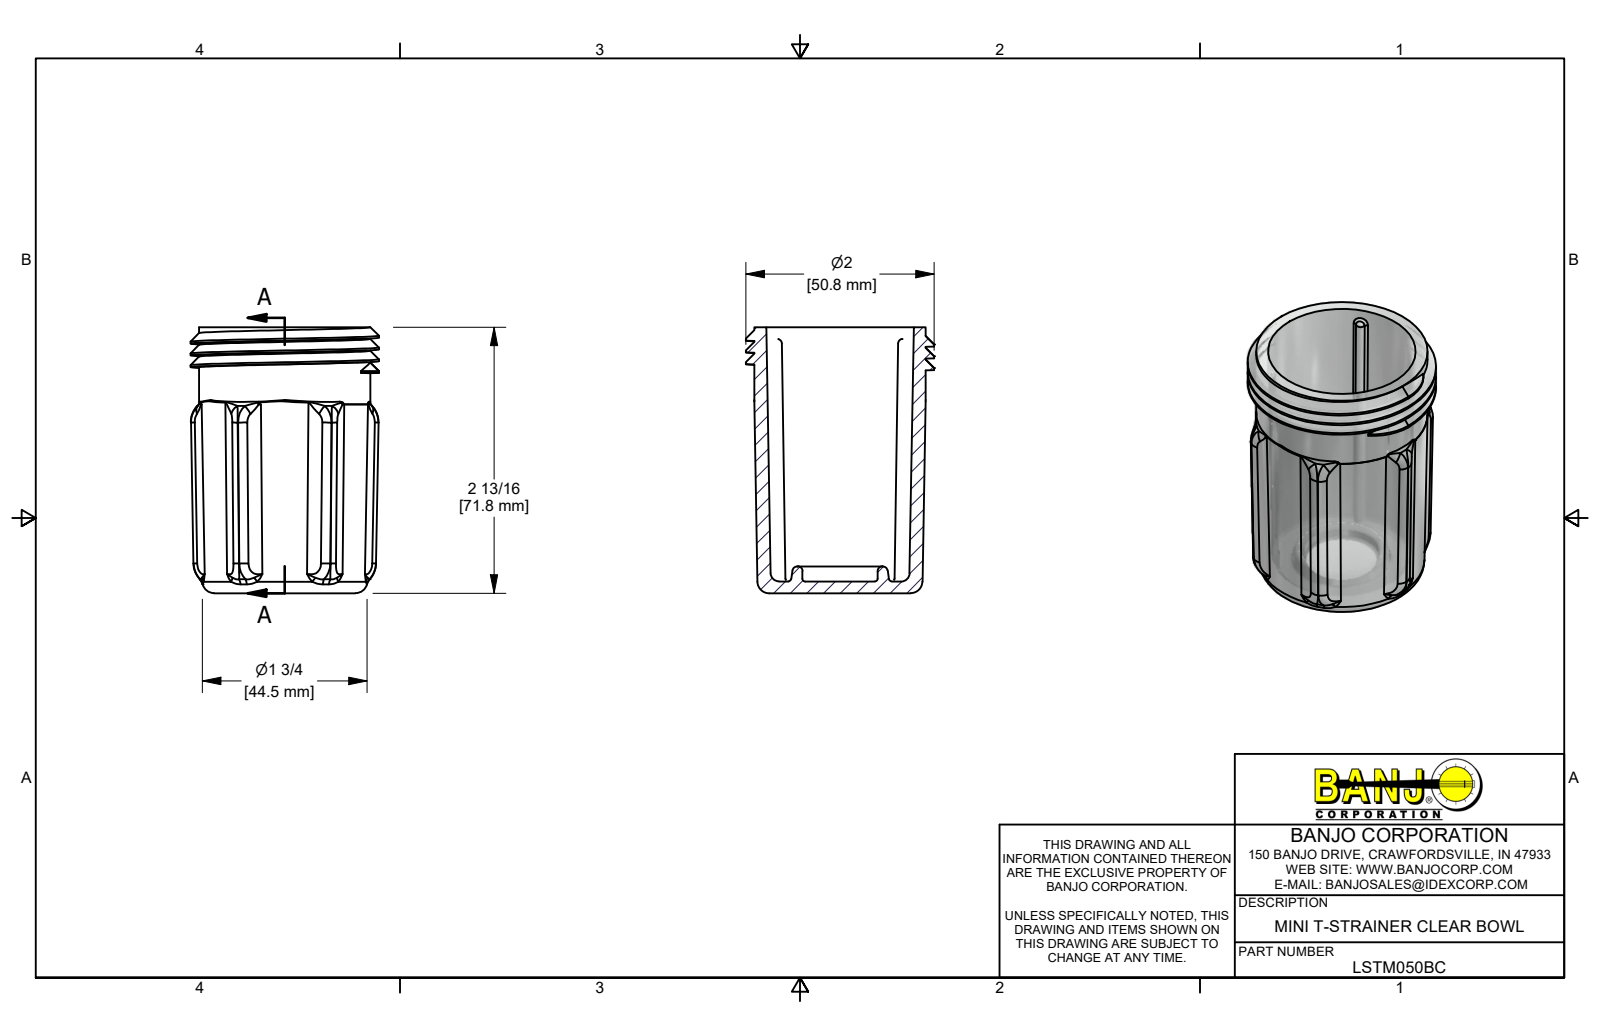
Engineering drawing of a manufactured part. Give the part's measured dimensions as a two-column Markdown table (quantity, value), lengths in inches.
| quantity | value |
| --- | --- |
| part name | LSTM050BC |
| STEP written by | Autodesk Inventor 2019 (AUTOMOTIVE_DESIGN) |
| units | inches |
| bodies | 1 solid, 198 faces (11 planar, 14 cylindrical, 173 other) |
| overall size | 2.825 × 2.002 × 2.002 |
| volume | 2.64 in³ |
| surface area | 37.39 in² |
| round holes (diameter × count) | 0.8 × 1 |
| round bosses / shafts (diameter × count) | 2.001 × 1, 1.82 × 1 |
| partial cylindrical surfaces (radius × count) | 0.05 × 3, 0.546 × 1 |
| main face-to-face distances | 0.125, 2.825, 2.7, 0.285, 0.16, 2.54 |
